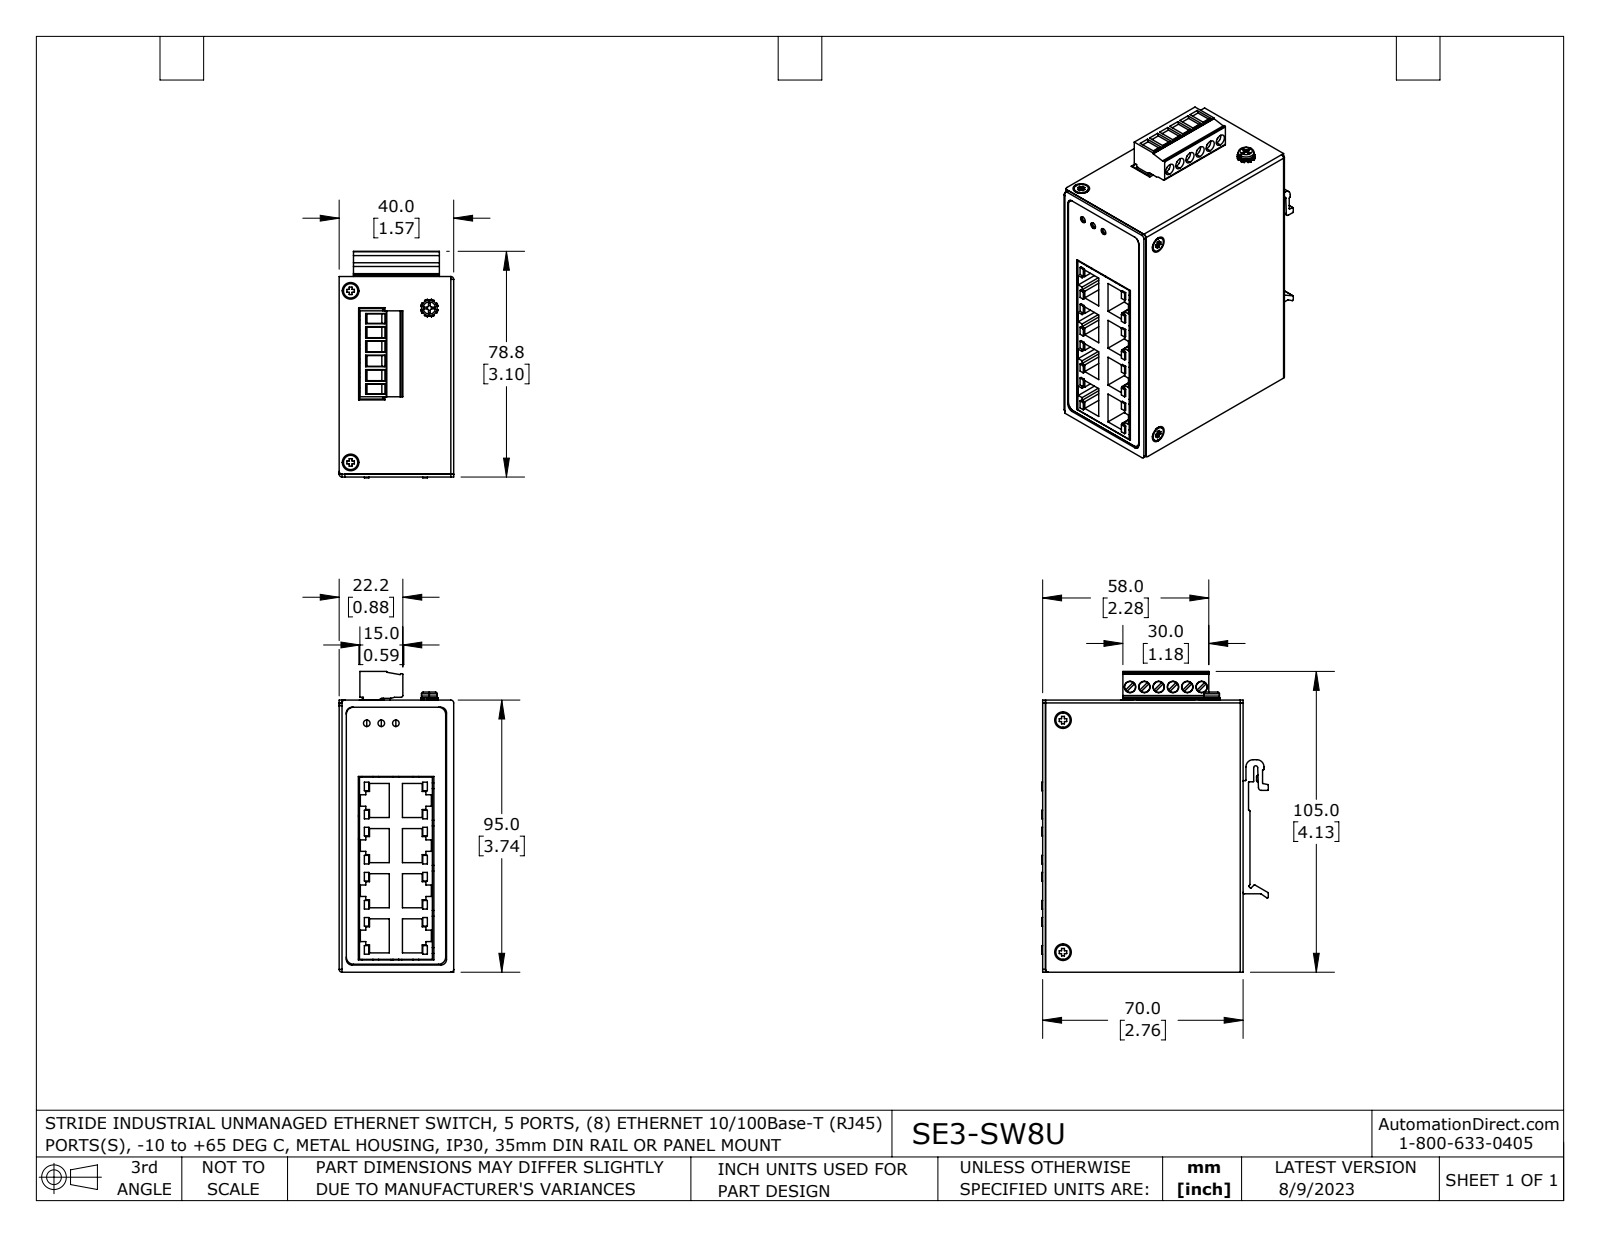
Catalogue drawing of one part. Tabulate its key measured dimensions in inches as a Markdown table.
| quantity | value |
| --- | --- |
| part name | cet2-0800 fxt from this orig TB ext1 coord fxt |
| STEP written by | SolidWorks 2021 (AUTOMOTIVE_DESIGN) |
| units | inches |
| bodies | 22 solids, 2007 faces (1145 planar, 610 cylindrical, 252 other) |
| overall size | 4.134 × 3.114 × 1.575 |
| volume | 4.443 in³ |
| surface area | 125.4 in² |
| round holes (diameter × count) | 0.157 × 15, 0.079 × 14, 0.118 × 5, 0.091 × 3, 0.097 × 3, 0.138 × 3, 0.096 × 2, 0.059 × 1, 0.096 × 1 |
| round bosses / shafts (diameter × count) | 0.197 × 9, 0.094 × 9, 0.149 × 6, 0.157 × 5, 0.11 × 5, 0.165 × 3, 0.157 × 3, 0.149 × 3 |
| partial cylindrical surfaces (radius × count) | 0.004 × 79, 0.039 × 26, 0.008 × 21, 0.008 × 10, 0.118 × 10, 0.098 × 7, 0.034 × 6, 0.115 × 6 |
| main face-to-face distances | 0.039, 0.02, 1.535, 1.516, 3.701, 2.697, 0.059, 1.575, 1.476, 1.496 |
| hole center spacings | 0.197, 0.394, 0.66, 0.591, 2.953, 0.2, 0.419, 0.726 |
